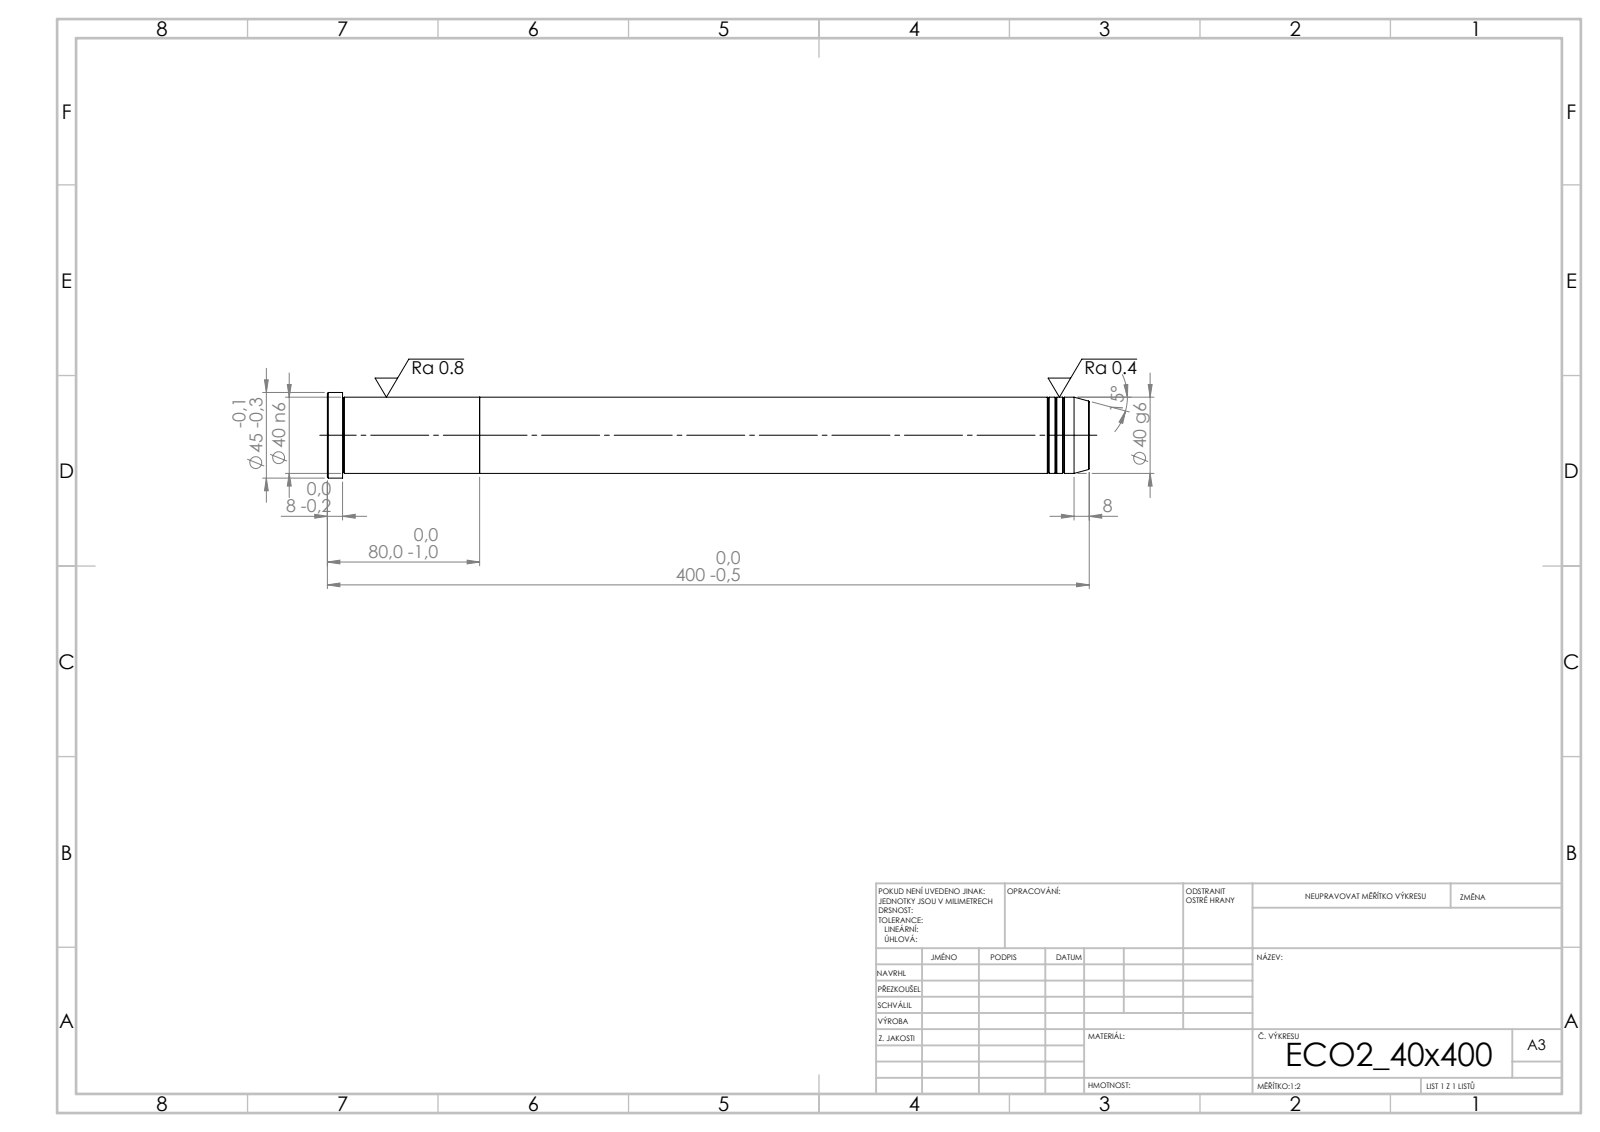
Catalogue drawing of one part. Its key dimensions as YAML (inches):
step_written_by: "SolidWorks 2019 (CONFIG_CONTROL_DESIGN)"
units: inches
bodies: {solids: 2, faces: 39, planar: 5, cylindrical: 12, other: 22}
overall_size: [15.748, 1.772, 1.772]
volume: 30.76
surface_area: 86.85
round_bosses_or_shafts:
  - {diameter: 1.772, count: 1}
  - {diameter: 1.575, count: 1}
face_to_face_distances: [3.15, 12.598, 15.748, 15.433, 2.835, 0.315]
